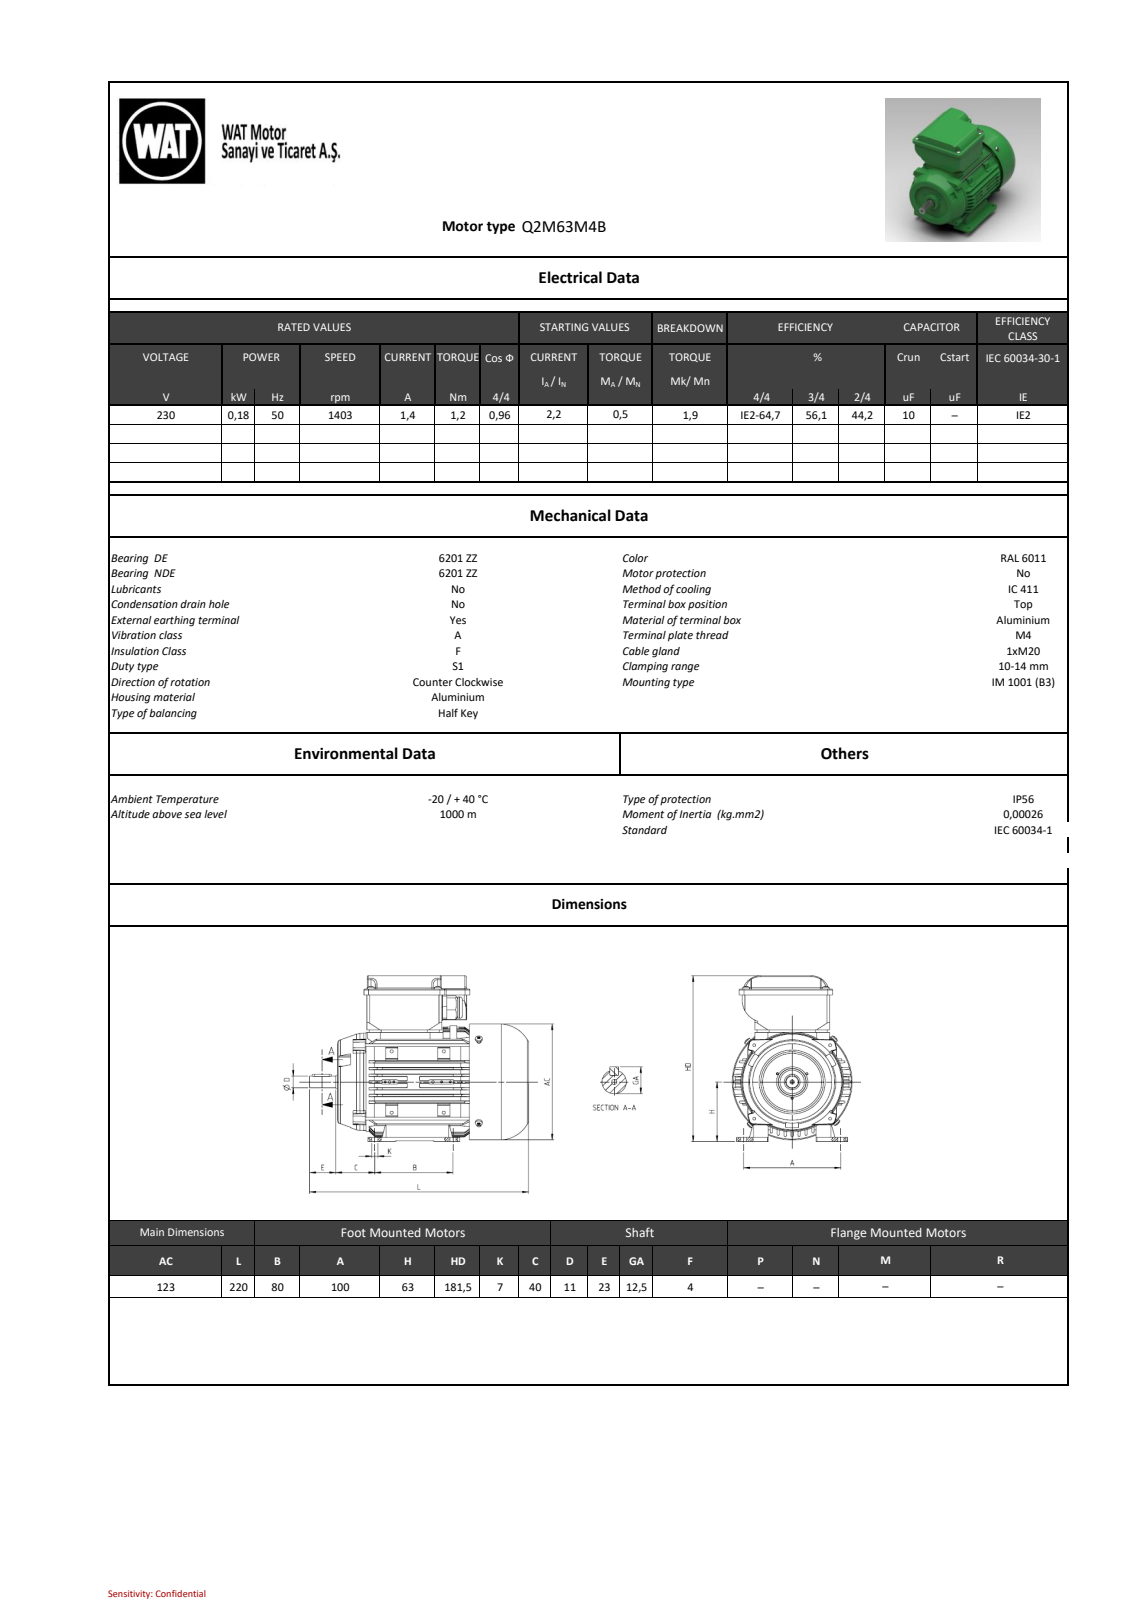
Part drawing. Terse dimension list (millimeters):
name: BY6424130xx_004-TKK_QM63-80; BY6434017xx_004-TK_QM63-80; BY6423003xx_006-FAN_KAPAGI_QS63; 641304740_AZ-KAMA PARALEL A 4x4x16 St50 DIN6885 (+8 more)
written by: SIEMENS PLM Software NX2206.8101 (AUTOMOTIVE_DESIGN)
unit: mm
bodies: 36 solids, 2363 faces (1201 planar, 856 cylindrical, 306 other)
size: 219.47 × 181.5 × 123
volume: 585 154 mm³; area: 418 504 mm²
holes: 10× ⌀3.65, 8× ⌀4.5, 6× ⌀2.5, 5× ⌀3.3, 4× ⌀3.5, 4× ⌀4.2, 4× ⌀4.65, 4× ⌀4.8, 3× ⌀3, 2× ⌀7, 1× ⌀5, 1× ⌀8
bosses: 8× ⌀8, 8× ⌀4, 8× ⌀3, 1× ⌀123, 1× ⌀70, 1× ⌀30, 1× ⌀25.28, 1× ⌀18
rounds: 212× R0.5, 127× R1, 60× R2, 20× R2.5, 10× R5, 9× R3, 9× R5.5, 8× R1.5
face distances: 3, 7, 4.5, 4, 1, 7.02, 27.96, 1.5, 10.5, 2.5
hole spacings: 55, 54, 54.45, 77, 0.61, 62.8, 63, 66.91
